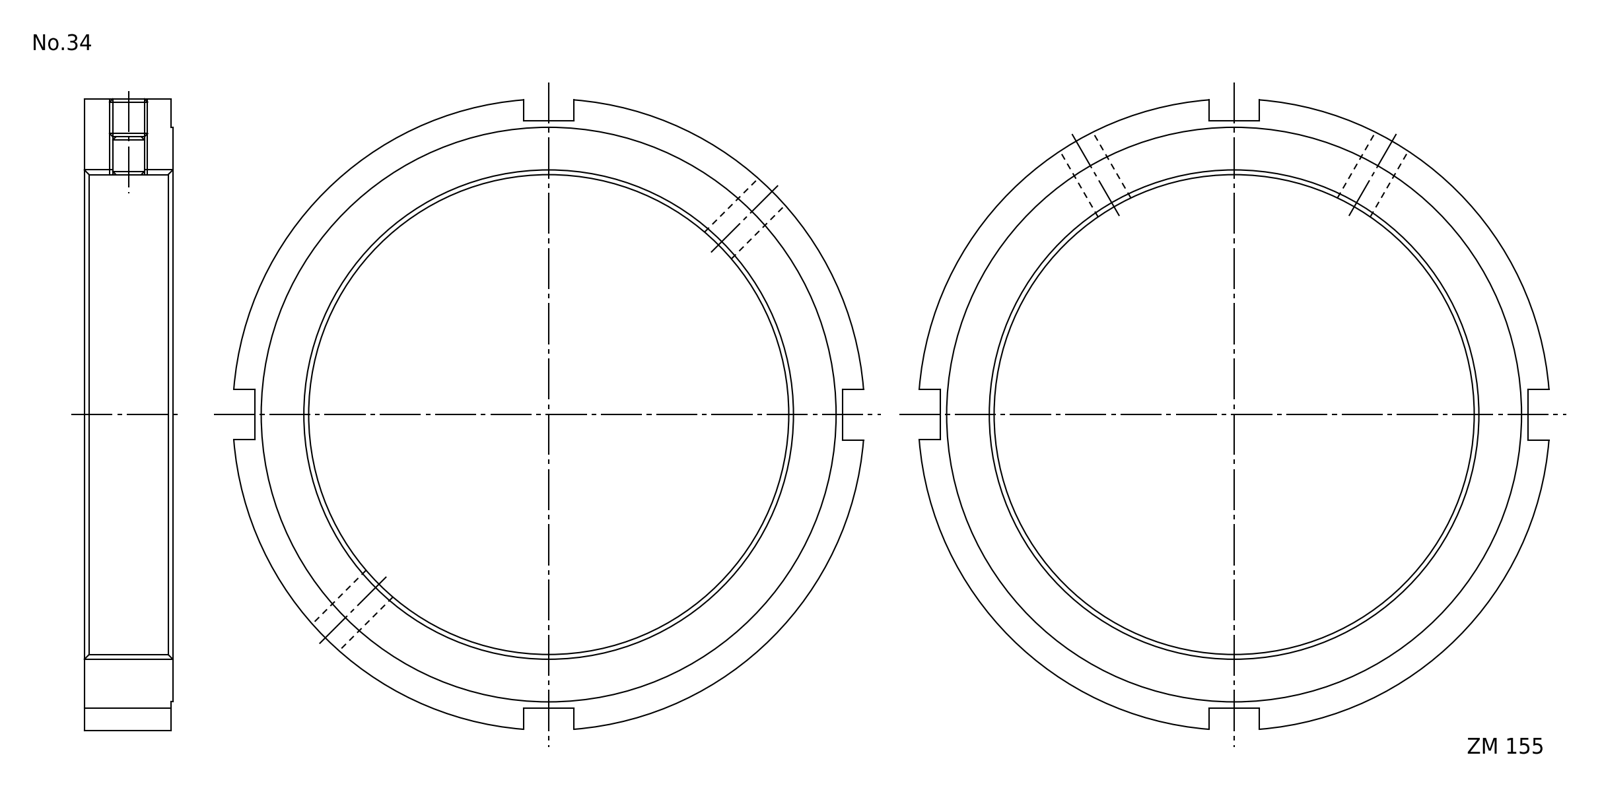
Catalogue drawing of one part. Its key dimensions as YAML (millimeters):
part_name: "FKD ZM155"
step_written_by: "Autodesk Inventor 2011 (AUTOMOTIVE_DESIGN)"
units: millimeters
bodies: {solids: 1, faces: 23, planar: 15, cylindrical: 8, other: 0}
overall_size: [199.36, 199.36, 28]
volume: 332867
surface_area: 57987
round_holes:
  - {diameter: 10.11, count: 2}
  - {diameter: 155, count: 1}
round_bosses_or_shafts:
  - {diameter: 200, count: 1}
  - {diameter: 182, count: 1}
face_to_face_distances: [28, 0.5, 27.5, 85, 101, 186, 16]
